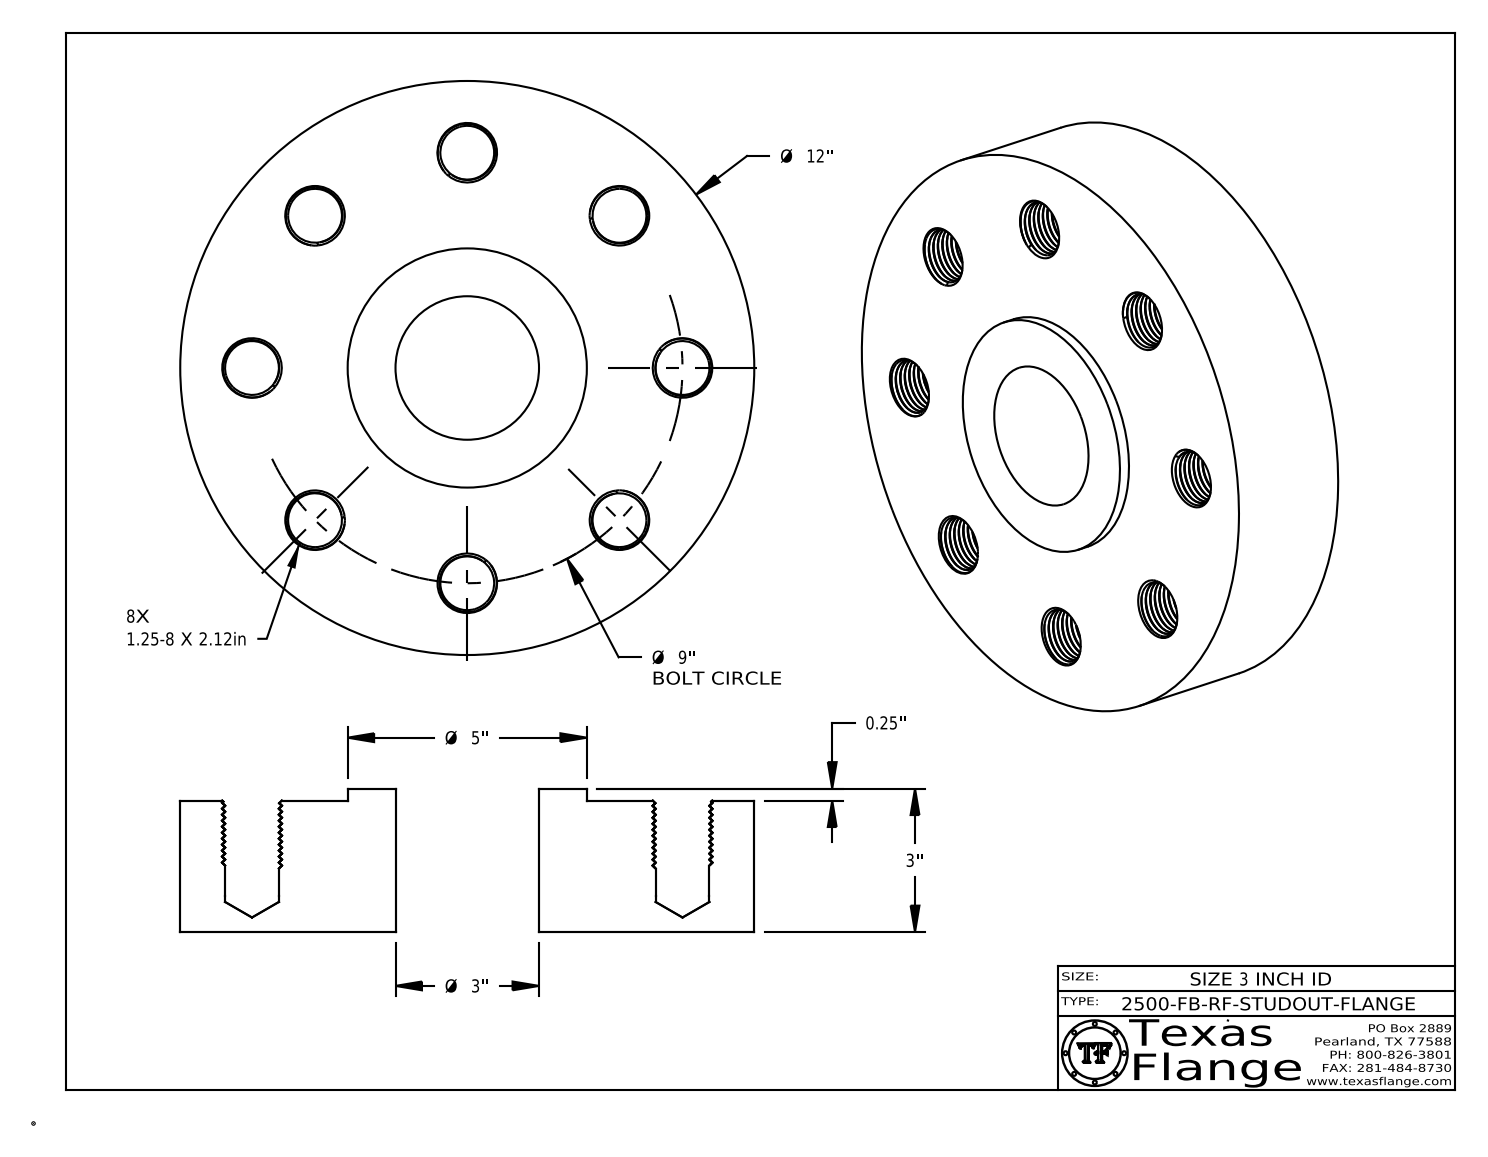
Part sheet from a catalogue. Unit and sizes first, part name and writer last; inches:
Units: inches
Overall size (bounding box): 12 × 12 × 3
Round holes (diameter × count): ⌀1.125 ×8, ⌀1 ×1, ⌀3 ×1
Round bosses / shafts (diameter × count): ⌀0.061 ×8, ⌀12 ×1, ⌀5 ×1, ⌀0.788 ×1
Main face-to-face distances: 2.75, 0.25, 3, 2.985, 2.735, 0.015, 0.298, 0.293, 0.054, 0.248
Hole centre spacings: 3.444, 4.5, 6.364, 8.315, 9, 9
Volume: 275.7 in³ · Surface area: 427 in²
Bodies: 1 solid, 1018 faces (368 planar, 218 cylindrical, 432 other)
Part name (STEP PRODUCT): 3-2500-FB-RF-STUDOUT-FLANGE
STEP written by: CATIA V5 STEP AP214 (AUTOMOTIVE_DESIGN)
